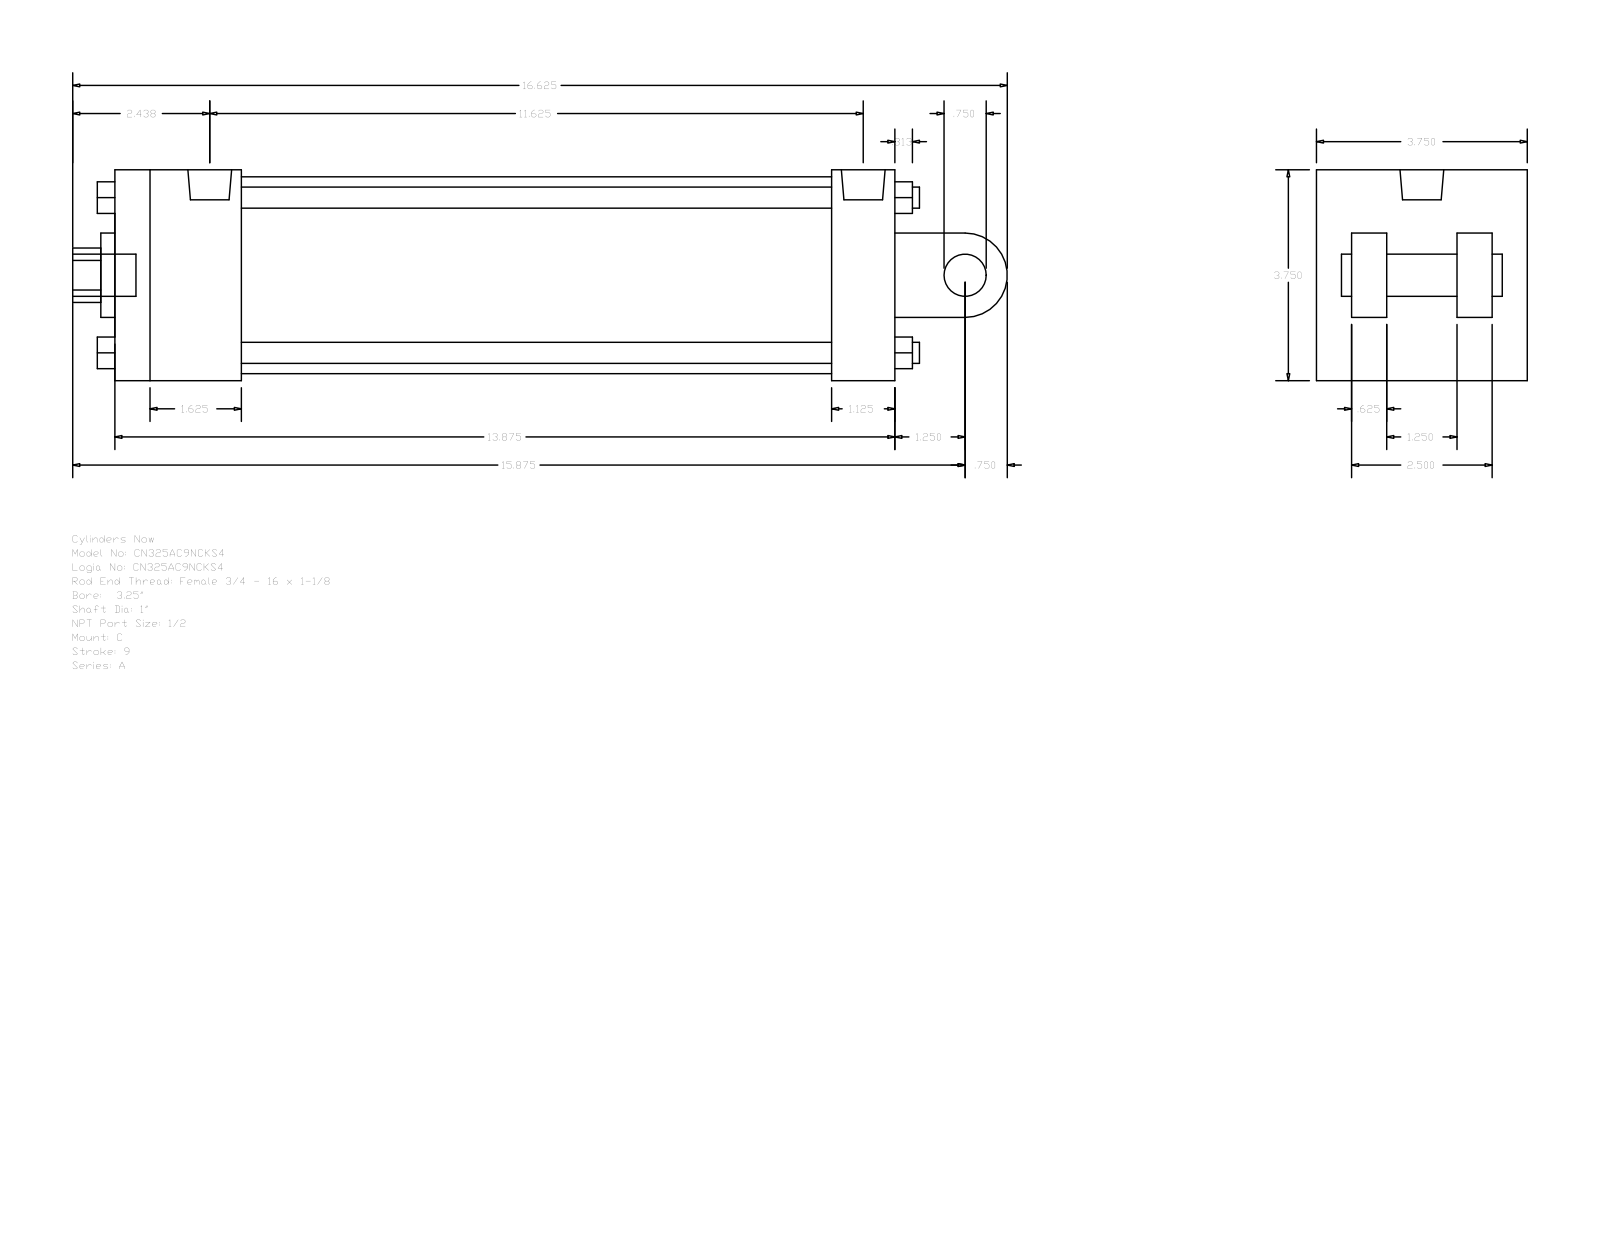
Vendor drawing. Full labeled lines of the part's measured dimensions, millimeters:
Part name (STEP PRODUCT): A_C__0325_1
STEP written by: GSSL Pune (CONFIG_CONTROL_DESIGN)
Units: millimetres
Bodies: 0 solids, 135 faces (102 planar, 33 cylindrical, 0 other)
Overall size (bounding box): 422.27 × 95.25 × 95.25
Round holes (diameter × count): ⌀8.73 ×2, ⌀19.77 ×1, ⌀25.4 ×1, ⌀38.1 ×1, ⌀88.9 ×1
Round bosses / shafts (diameter × count): ⌀9.53 ×4, ⌀19.05 ×2, ⌀8.73 ×2, ⌀19.77 ×1
Partial cylindrical surfaces — rounded edges, fillets, slot ends (radius × count): R12.29 ×1, R19.05 ×1
Main face-to-face distances: 95.24, 352.43, 15.87, 63.5, 47.63, 79.37, 31.74, 66.67, 323.85, 28.58
Hole centre spacings: 3.18
